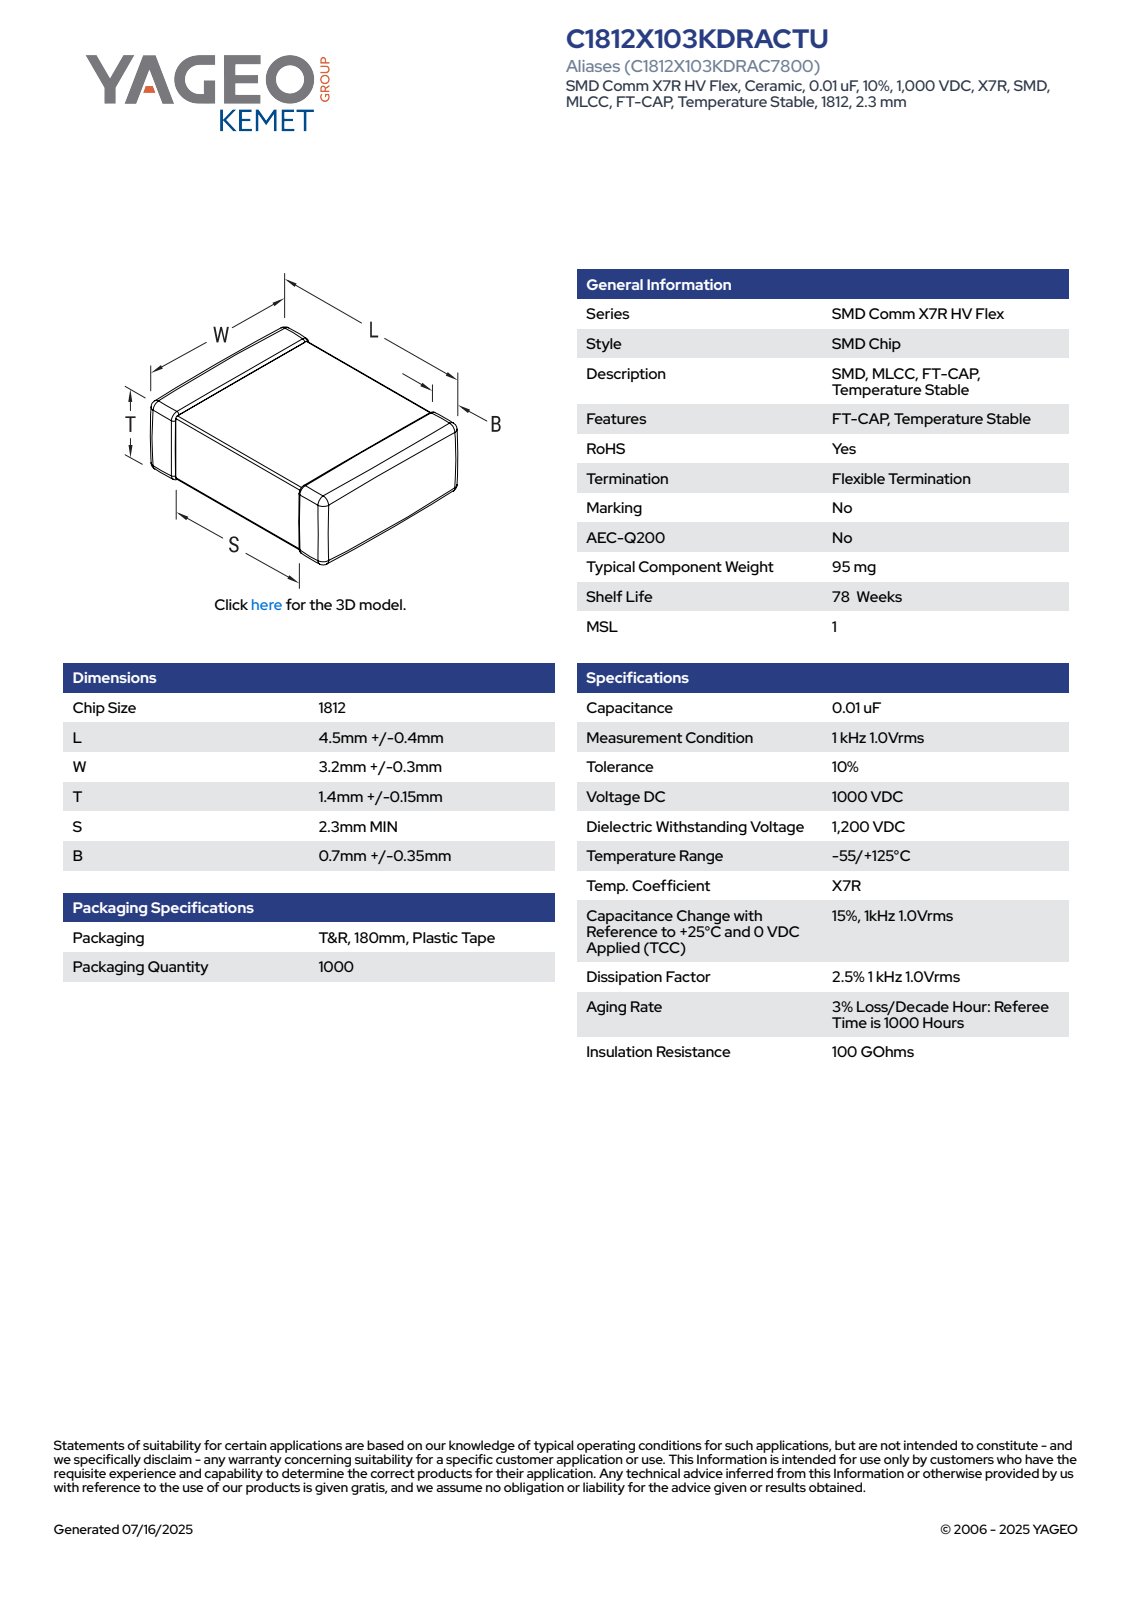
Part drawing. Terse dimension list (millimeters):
name: CCS_CCSTDNOS_1812_L4.9W3.5T1.55B1.05
written by: SolidWorks 2014 (AUTOMOTIVE_DESIGN)
unit: mm
bodies: 4 solids, 125 faces (71 planar, 38 cylindrical, 16 other)
size: 4.9 × 3.5 × 1.55
volume: 25 mm³; area: 59 mm²
face distances: 1.48, 1.41, 1.55, 3.43, 4.9, 3.36, 3.5, 1.42, 1.94, 1.49
